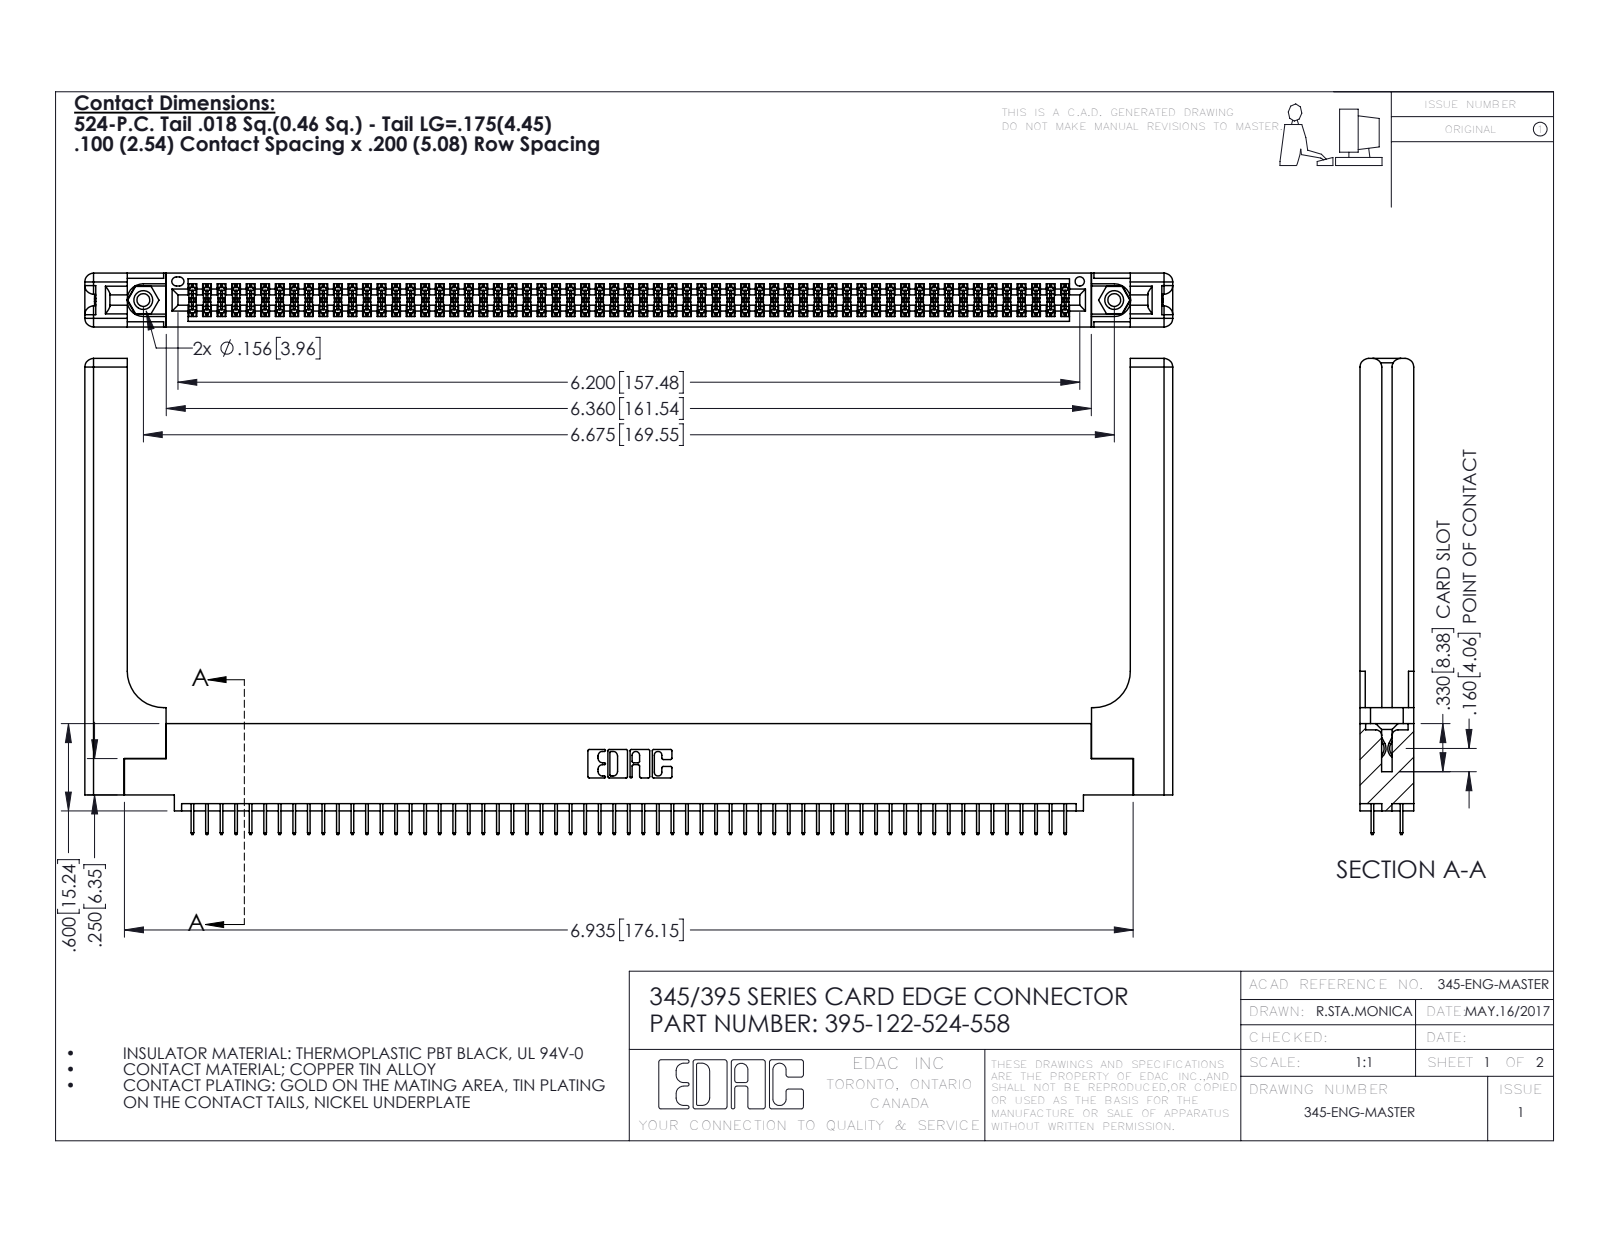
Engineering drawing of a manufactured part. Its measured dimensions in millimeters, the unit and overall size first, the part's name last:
Units: millimetres
Overall size (bounding box): 190 × 83.1 × 9.4
Round holes (diameter × count): ⌀2.3 ×2, ⌀3.2 ×2, ⌀4 ×2, ⌀1.6 ×1
Round bosses / shafts (diameter × count): ⌀3.9 ×2
Partial cylindrical surfaces — rounded edges, fillets, slot ends (radius × count): R0.2 ×183, R0.3 ×22, R1.5 ×16, R0.2 ×6, R0.8 ×6, R0.7 ×3, R0.4 ×2, R0.5 ×2
Main face-to-face distances: 1.8, 7.6, 9.4, 5.1, 2.5, 6.9, 0.6, 5.7, 1.8, 3.8
Hole centre spacings: 6.9, 163.6, 169.5
Volume: 26 840 mm³ · Surface area: 32 190 mm²
Bodies: 127 solids, 6974 faces (4990 planar, 1924 cylindrical, 60 other)
Part name (STEP PRODUCT): 395-122-524-558; 345-292-001_345-293-124; 345-250-001_345-250-001-102; 345-220-058_345-220-058 (+1 more)
STEP written by: SolidWorks 2016 (CONFIG_CONTROL_DESIGN)
